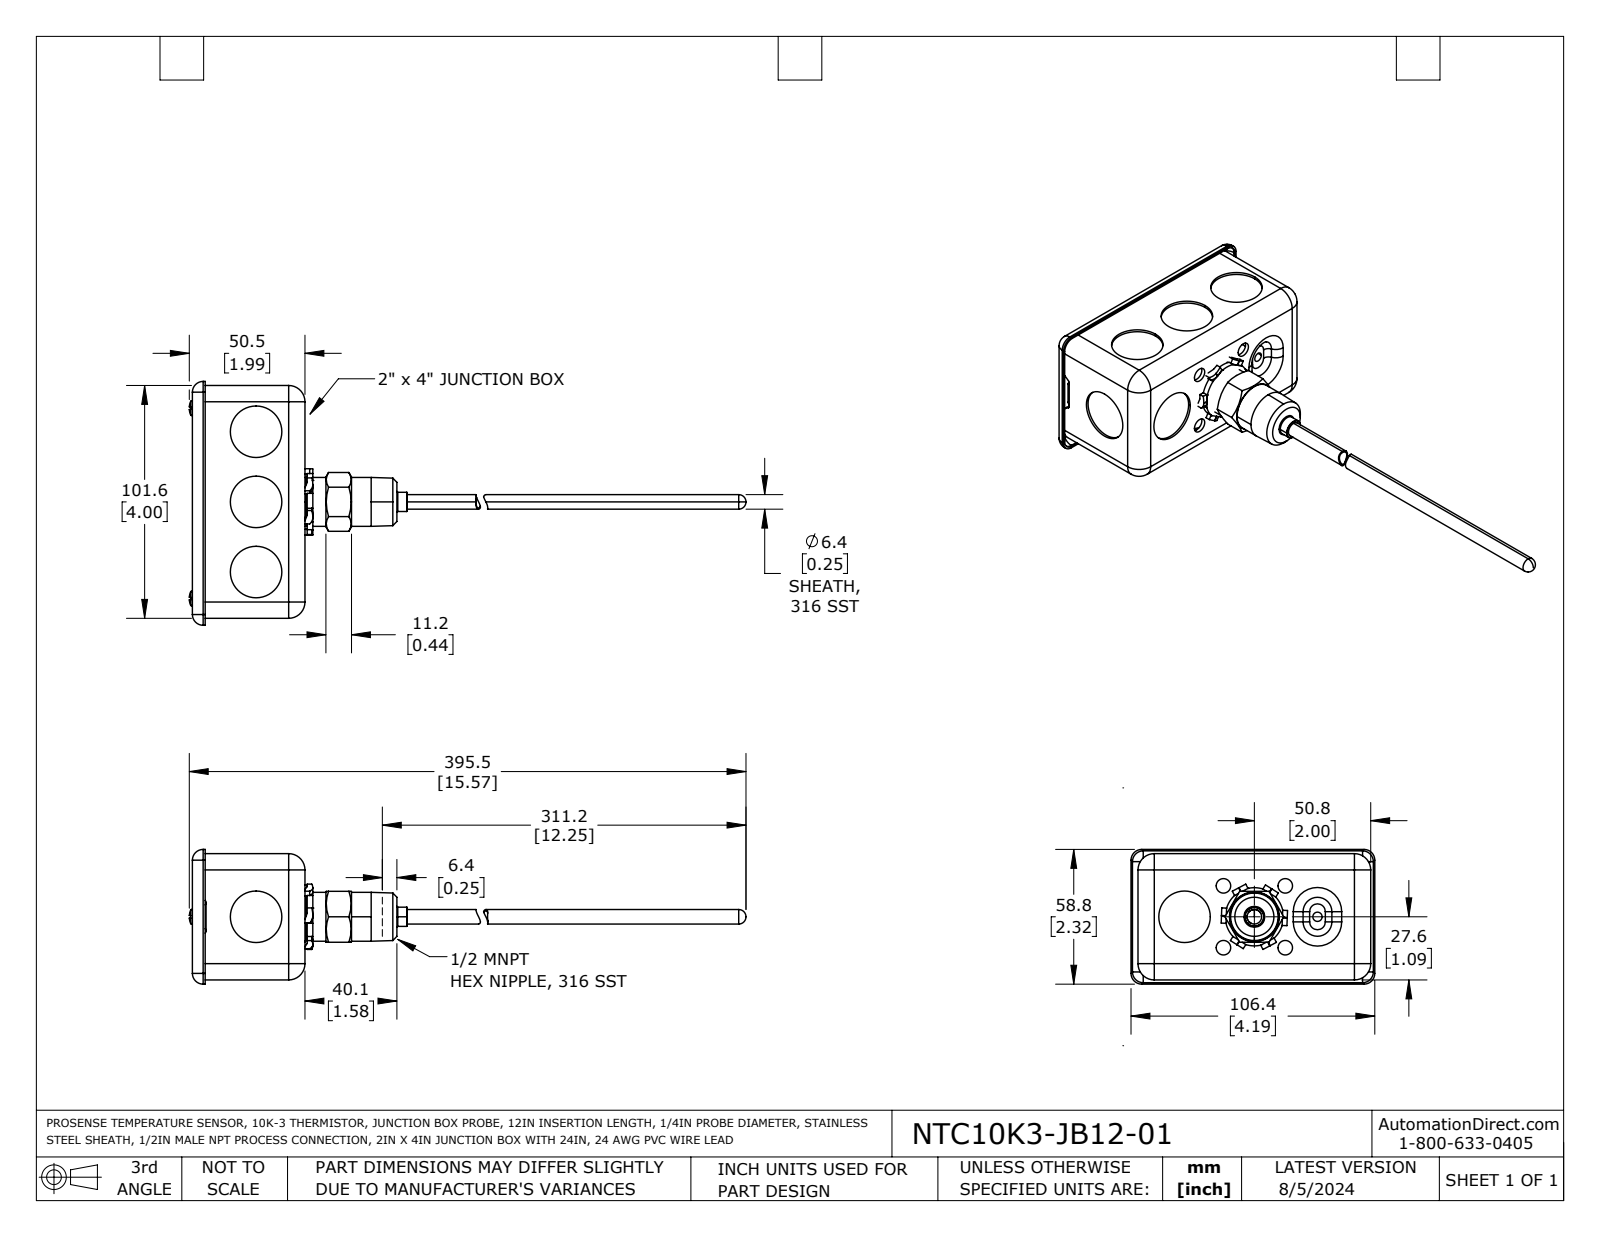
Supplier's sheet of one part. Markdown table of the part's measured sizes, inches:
| quantity | value |
| --- | --- |
| part name | NTC10K3-JB12-01 |
| STEP written by | SolidWorks 2021 (AUTOMOTIVE_DESIGN) |
| units | inches |
| bodies | 5 solids, 365 faces (154 planar, 145 cylindrical, 66 other) |
| overall size | 15.513 × 4.19 × 2.315 |
| volume | 3.201 in³ |
| surface area | 110.3 in² |
| round holes (diameter × count) | 0.885 × 6, 0.25 × 4, 0.115 × 2, 0.16 × 1, 0.21 × 1, 0.253 × 1, 0.438 × 1 |
| round bosses / shafts (diameter × count) | 0.136 × 2, 0.84 × 1, 0.33 × 1, 0.25 × 1 |
| partial cylindrical surfaces (radius × count) | 0.185 × 16, 0.245 × 8, 0.28 × 8, 0.174 × 6, 0.555 × 6, 0.045 × 4, 0.165 × 4, 0.07 × 2 |
| main face-to-face distances | 0.07, 0.03, 2.03, 2.1, 0.04, 0.1, 0.06, 1.805, 2, 2.13 |
| hole center spacings | 0.751, 1.062, 1.248, 2.254, 0.767, 0.854, 1.205, 1.502 |
